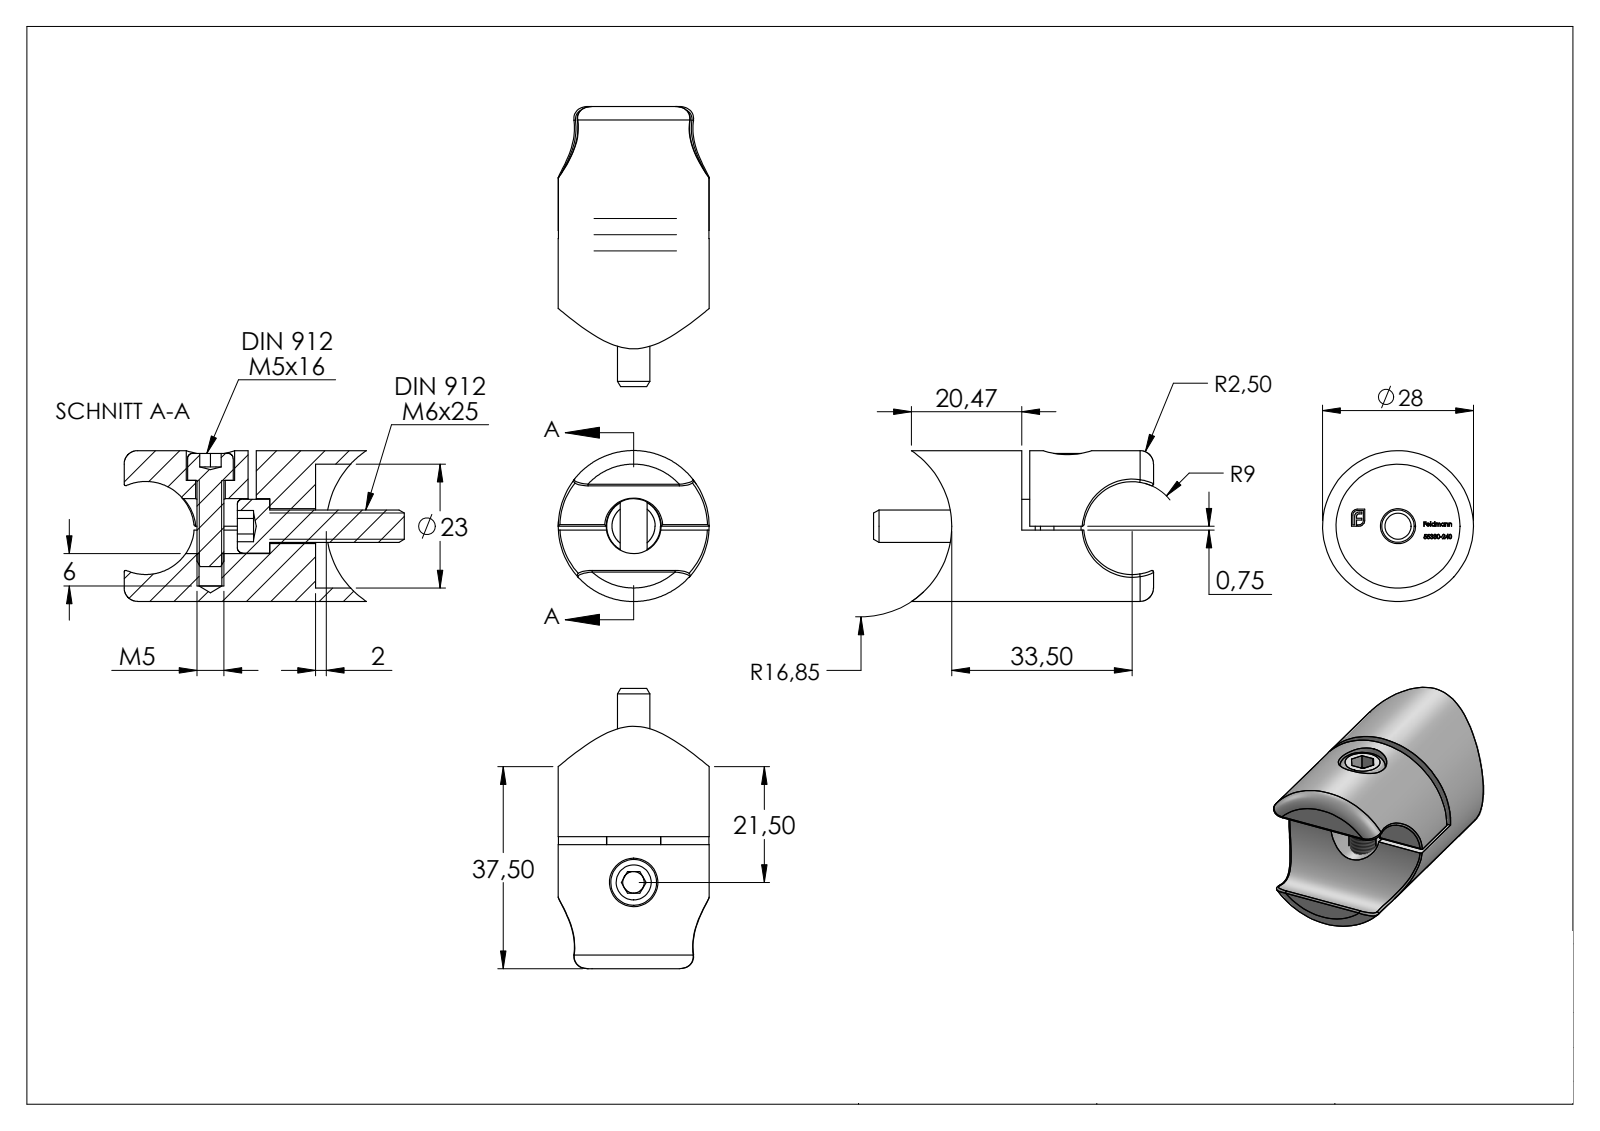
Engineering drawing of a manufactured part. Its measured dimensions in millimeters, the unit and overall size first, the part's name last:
Units: millimetres
Overall size (bounding box): 52 × 28 × 28
Round holes (diameter × count): ⌀4.2 ×1, ⌀5.5 ×1, ⌀6.5 ×1, ⌀9 ×1, ⌀10.2 ×1, ⌀23 ×1
Round bosses / shafts (diameter × count): ⌀28 ×1, ⌀10 ×1, ⌀8.5 ×1, ⌀6 ×1, ⌀5 ×1
Partial cylindrical surfaces — rounded edges, fillets, slot ends (radius × count): R0.3 ×3, R9 ×2, R16.85 ×1
Main face-to-face distances: 11, 1.5, 12.5, 8.5, 0.75, 4, 2.5, 9.25, 35.5, 27
Volume: 16 911 mm³ · Surface area: 8 129 mm²
Bodies: 4 solids, 374 faces (182 planar, 31 cylindrical, 161 other)
Part name (STEP PRODUCT): 5533X-240 Teil2; DIN 912 Konfig_DIN 912 M6x25; 5533X-240 Teil2_5533X-240 Teil2; 5533X-240 Teil1_55330-240 Teil1 (+4 more)
STEP written by: SolidWorks 2018 (CONFIG_CONTROL_DESIGN)
